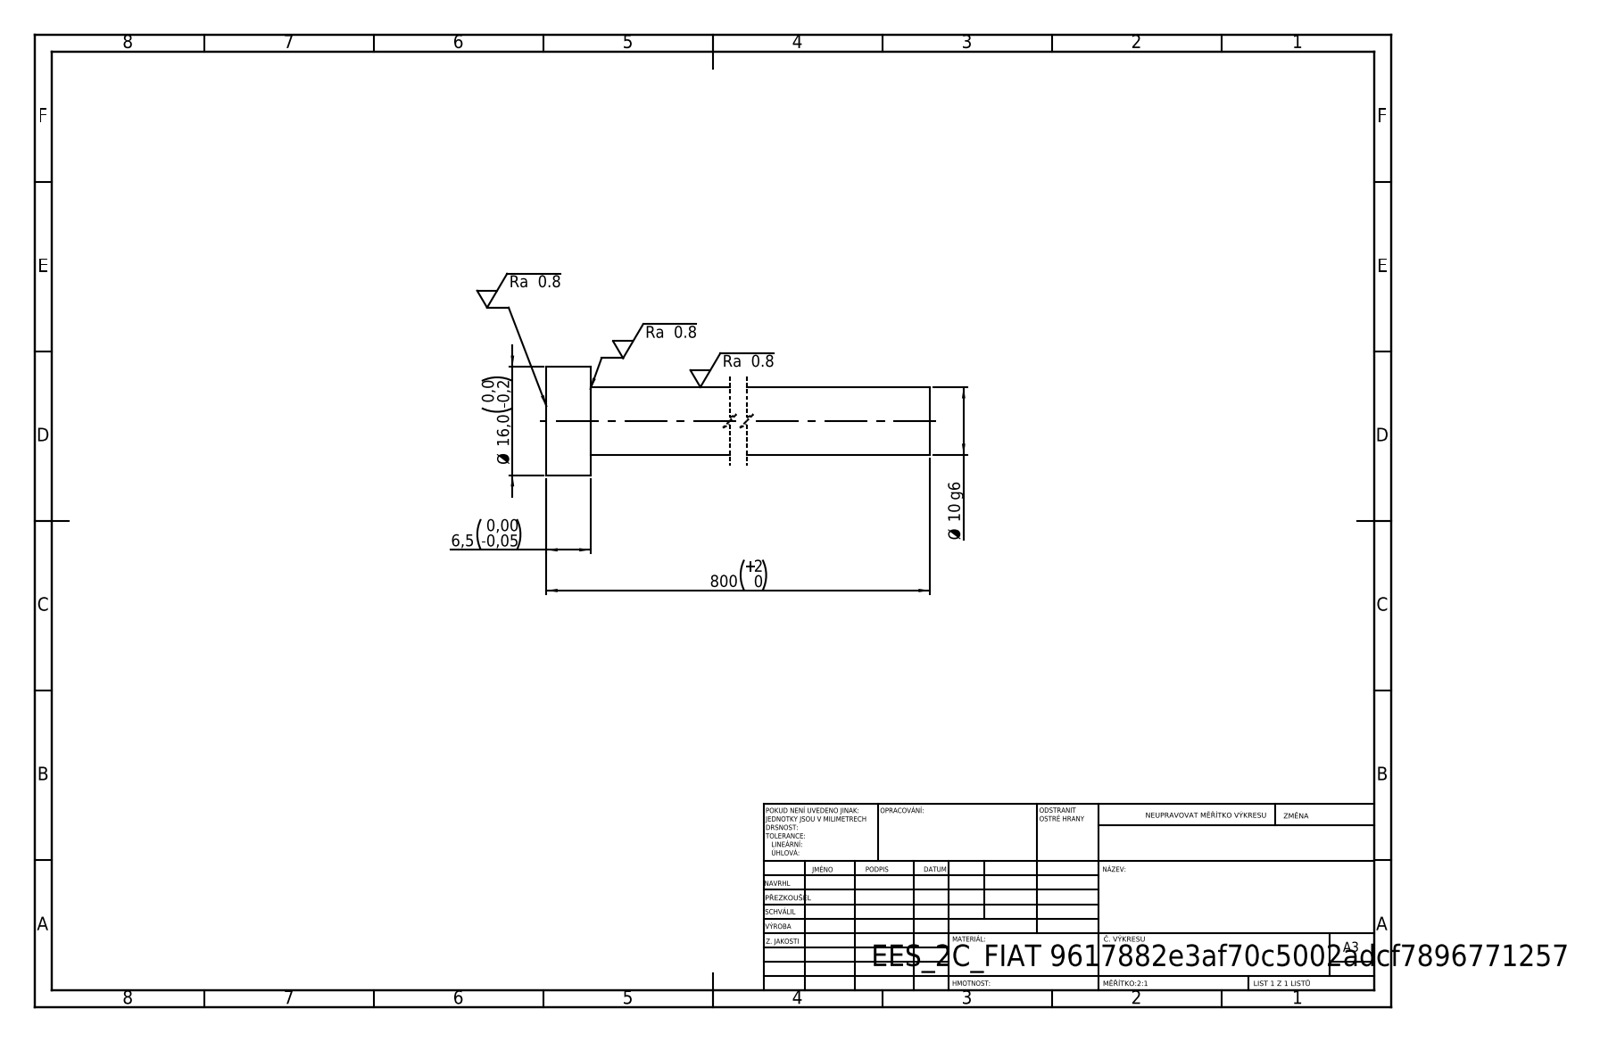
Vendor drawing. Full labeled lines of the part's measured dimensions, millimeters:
STEP written by: SolidWorks 2019 (CONFIG_CONTROL_DESIGN)
Units: millimetres
Bodies: 1 solid, 7 faces (3 planar, 4 cylindrical, 0 other)
Overall size (bounding box): 800 × 16 × 16
Volume: 63 628 mm³ · Surface area: 25 657 mm²
Round bosses / shafts (diameter × count): ⌀16 ×1, ⌀10 ×1
Main face-to-face distances: 6.5, 800, 793.5
